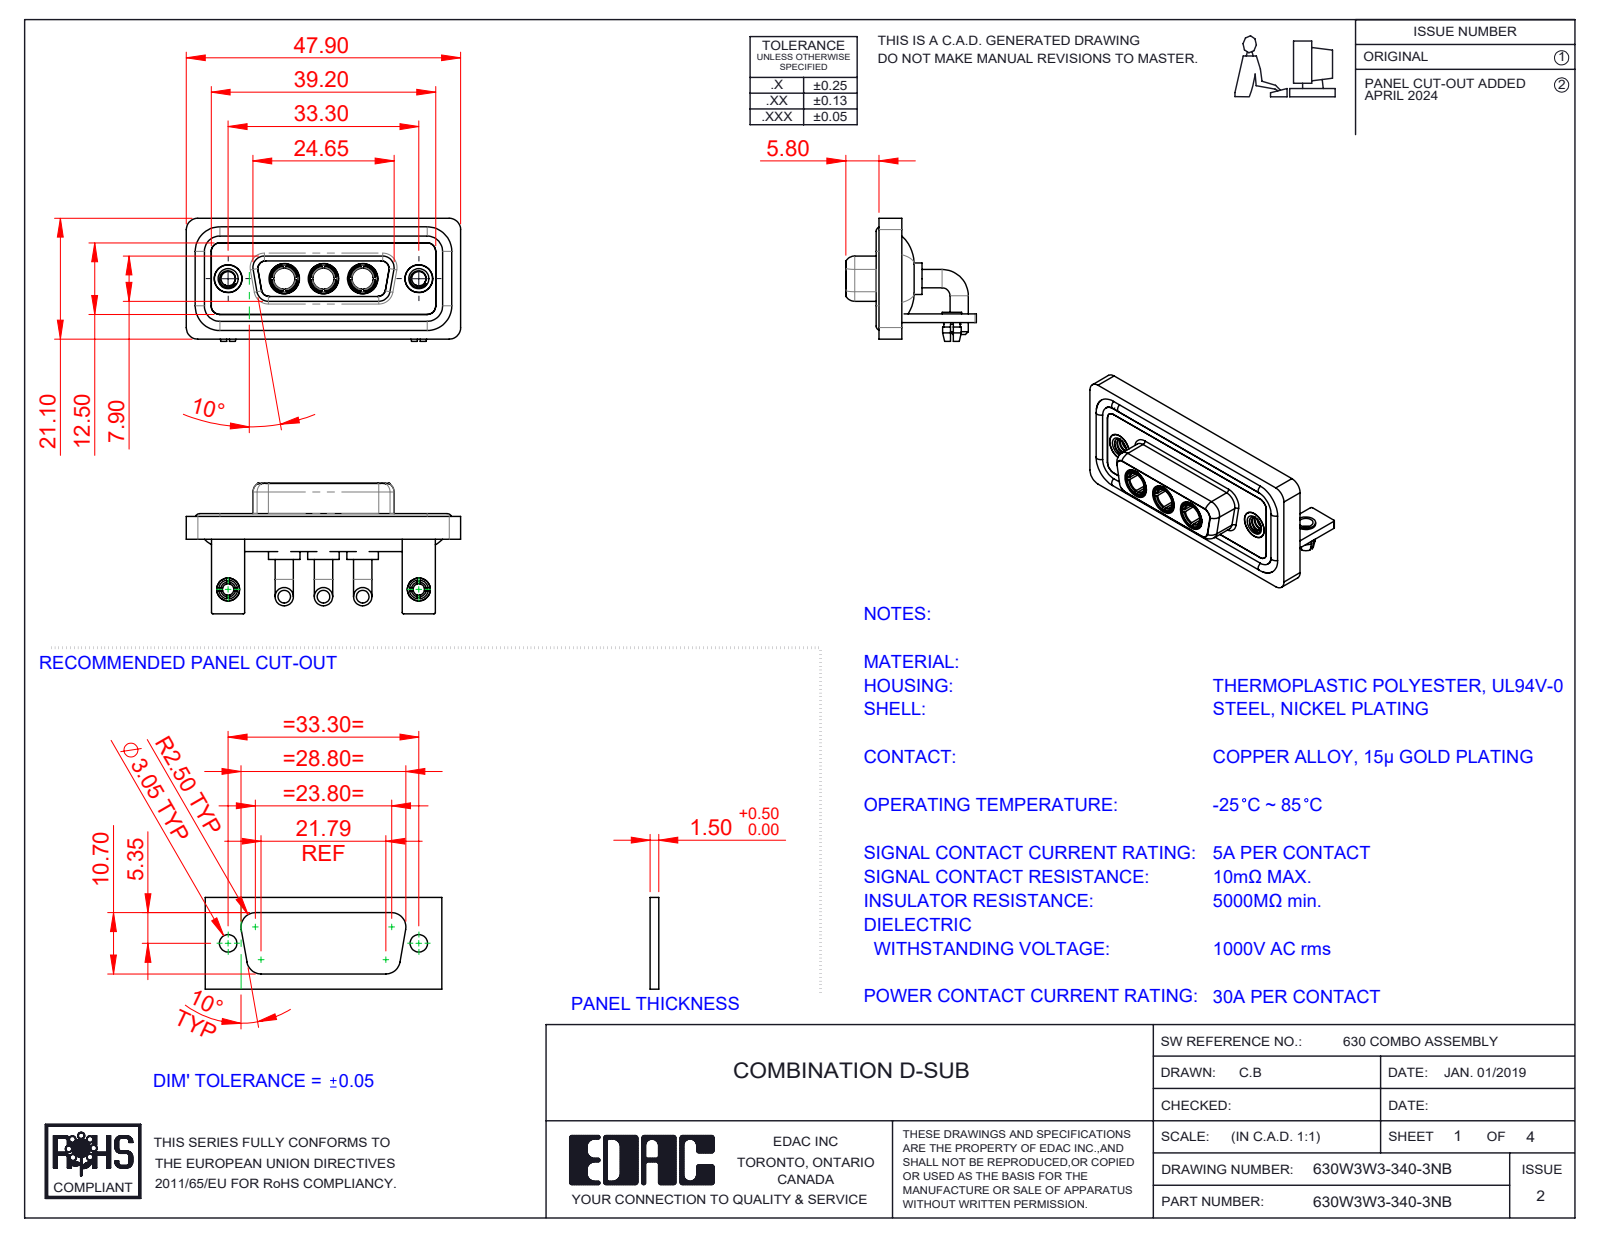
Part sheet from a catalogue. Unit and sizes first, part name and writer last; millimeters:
Units: millimetres
Overall size (bounding box): 47.9 × 22.8 × 21.5
Round holes (diameter × count): ⌀4.85 ×5, ⌀2.5 ×4, ⌀3.7 ×3, ⌀5.3 ×3, ⌀2 ×2, ⌀3.2 ×2, ⌀4 ×2, ⌀4.05 ×2, ⌀5 ×2
Round bosses / shafts (diameter × count): ⌀3.2 ×6, ⌀1.6 ×4, ⌀5.5 ×3, ⌀5.2 ×3, ⌀4.96 ×3, ⌀4.75 ×3, ⌀3.75 ×3, ⌀4.95 ×2
Partial cylindrical surfaces — rounded edges, fillets, slot ends (radius × count): R2 ×21, R1.5 ×18, R0.25 ×16, R1.35 ×12, R1.6 ×8, R0.5 ×5, R0.6 ×4, R0.65 ×4
Main face-to-face distances: 0.4, 2.9, 1.5, 1.8, 3.7, 1.1, 4.1, 1.6, 2.5, 1.4
Hole centre spacings: 6.85, 9.8, 16.65, 23.5, 33.3, 13.7
Volume: 6 659 mm³ · Surface area: 10 976 mm²
Bodies: 17 solids, 754 faces (260 planar, 317 cylindrical, 177 other)
Part name (STEP PRODUCT): 630Combo Shell Rear_15 Contacts; Power Socket_30A RA; 630W3W3-340-3NB; 630Combo Housing_3W3 (+5 more)
STEP written by: SolidWorks 2023 (CONFIG_CONTROL_DESIGN)
